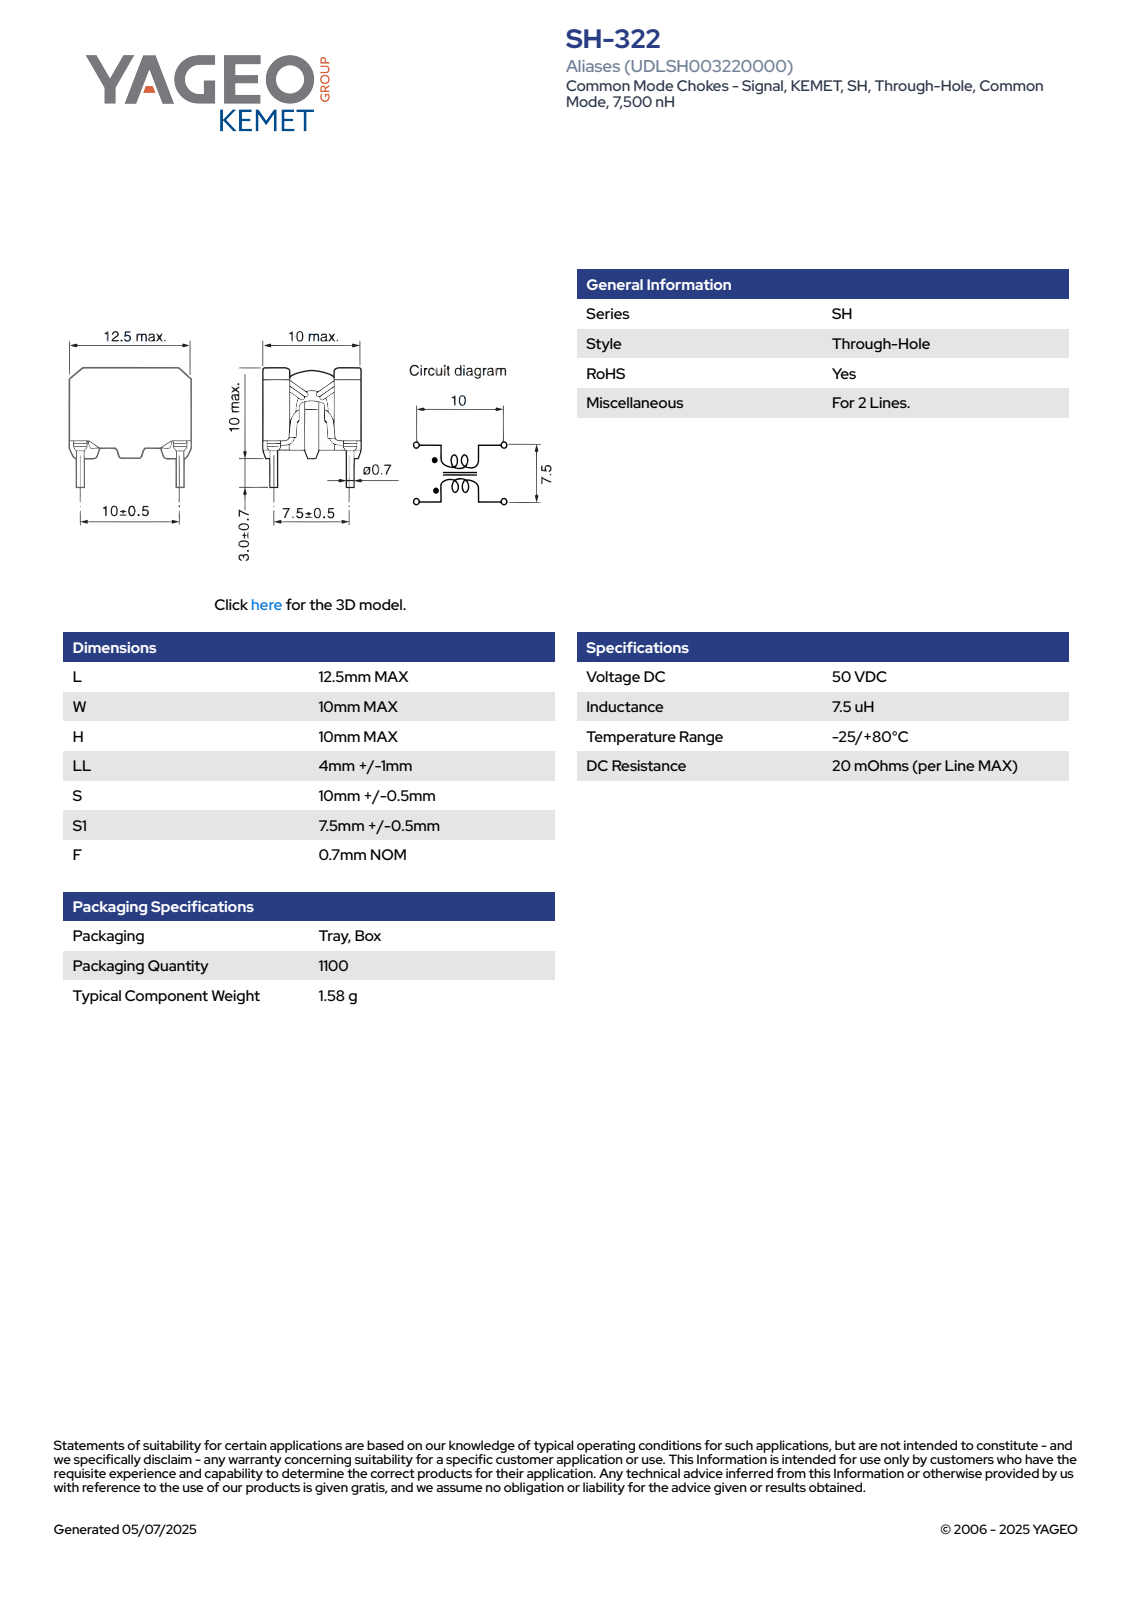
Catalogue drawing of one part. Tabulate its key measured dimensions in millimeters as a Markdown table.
| quantity | value |
| --- | --- |
| part name | IFC_NTSH3_L12.5W10H10 |
| STEP written by | SolidWorks 2014 (AUTOMOTIVE_DESIGN) |
| units | millimeters |
| bodies | 1 solid, 164 faces (101 planar, 63 cylindrical, 0 other) |
| overall size | 13.71 × 12.5 × 10 |
| volume | 839 mm³ |
| surface area | 1 041 mm² |
| round bosses / shafts (diameter × count) | 0.9 × 4, 0.7 × 4, 5.37 × 1 |
| partial cylindrical surfaces (radius × count) | 0.25 × 34, 3 × 1, 3.05 × 1 |
| main face-to-face distances | 1.75, 8.25, 10, 6.5, 2.86, 7.14, 1.11, 5.39, 12.5, 3.78 |
